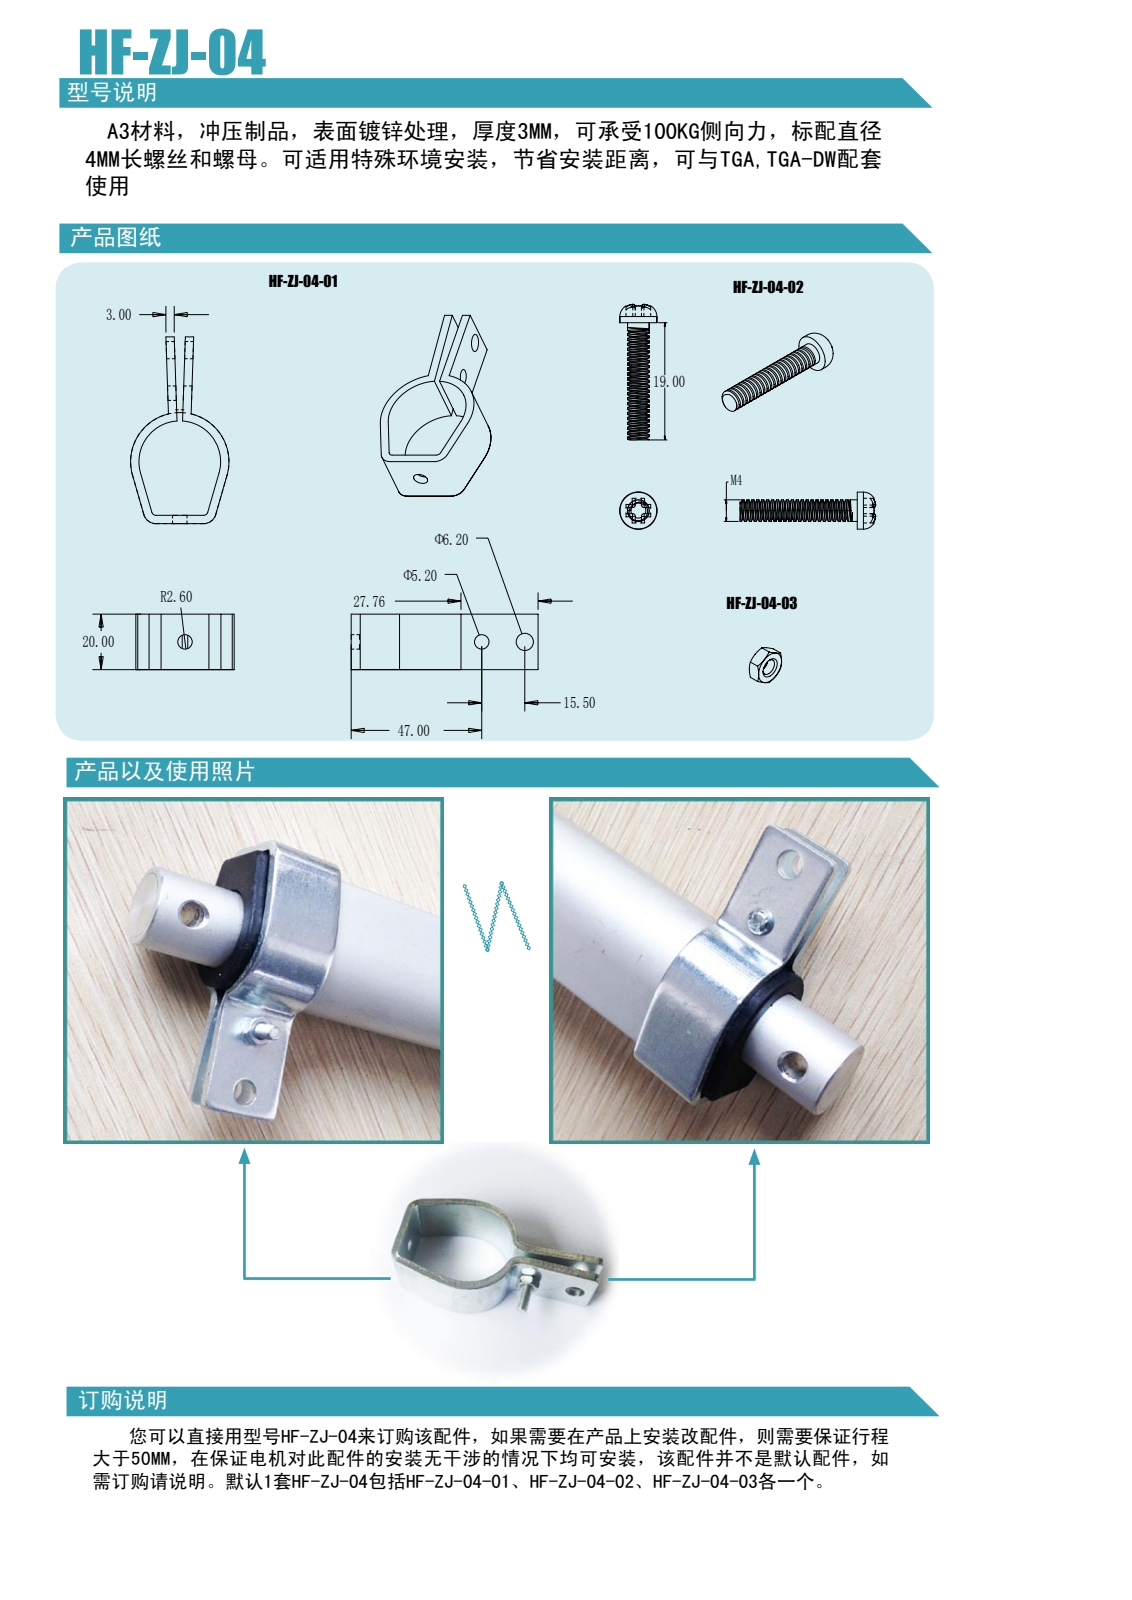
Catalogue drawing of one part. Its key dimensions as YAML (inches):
part_name: "ZJ-04"
step_written_by: "PRO/ENGINEER BY PARAMETRIC TECHNOLOGY CORPORATION, 2008380 (CONFIG_CONTROL_DESIGN)"
units: inches
bodies: {solids: 1, faces: 32, planar: 14, cylindrical: 18, other: 0}
overall_size: [67.28, 35.4, 20]
volume: 9666
surface_area: 7834
round_holes:
  - {diameter: 5.2, count: 2}
  - {diameter: 6.2, count: 1}
partial_cylinders:
  - {radius: 1.5, count: 2}
  - {radius: 4.5, count: 2}
  - {radius: 14.7, count: 1}
  - {radius: 17.7, count: 1}
face_to_face_distances: [3, 2.997, 20, 3, 2.995, 3.006, 64.28, 67.28]
hole_center_spacings: [15.5]
